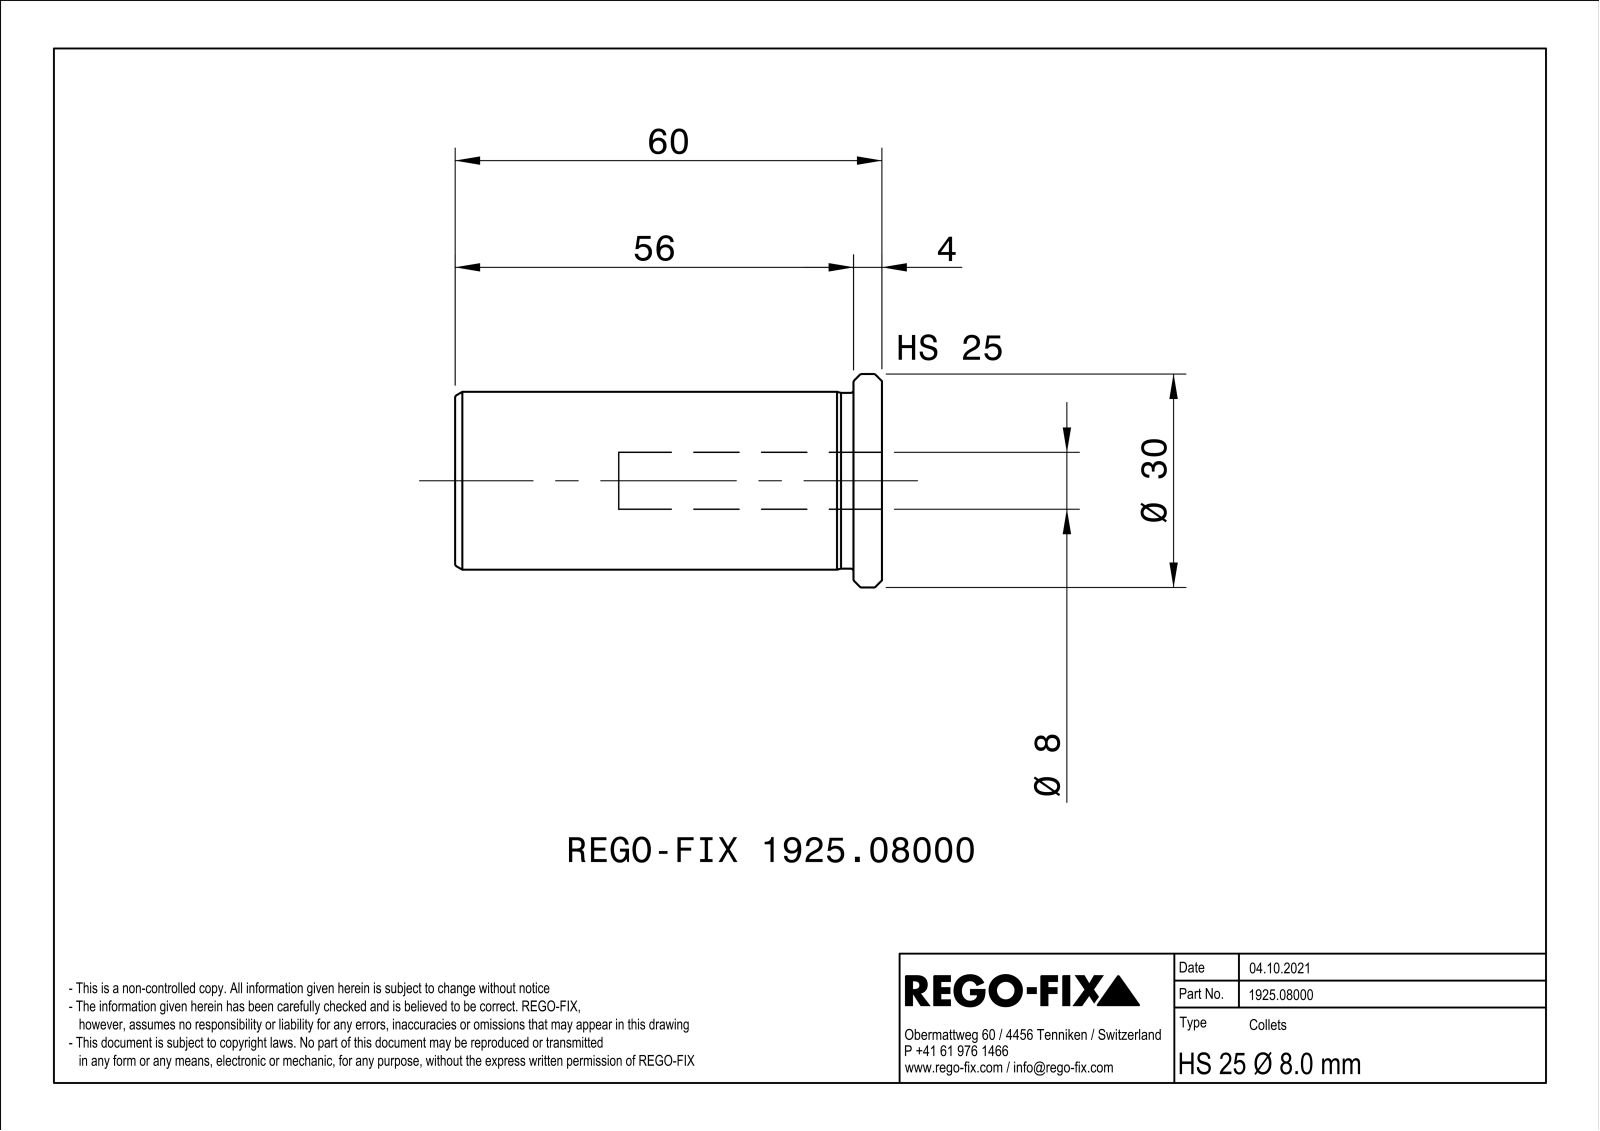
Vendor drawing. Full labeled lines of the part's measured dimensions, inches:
Part name (STEP PRODUCT): NOCUT
STEP written by: SIEMENS PLM Software Solid Edge ST10 (AUTOMOTIVE_DESIGN)
Units: inches
Bodies: 1 solid, 73 faces (22 planar, 12 cylindrical, 39 other)
Overall size (bounding box): 2.362 × 1.181 × 1.181
Volume: 1.376 in³ · Surface area: 15.27 in²
Round holes (diameter × count): ⌀0.315 ×1, ⌀0.394 ×1, ⌀0.807 ×1
Round bosses / shafts (diameter × count): ⌀1.181 ×1, ⌀0.984 ×1, ⌀0.972 ×1
Main face-to-face distances: 0.031, 0.157, 2.362, 2.205
